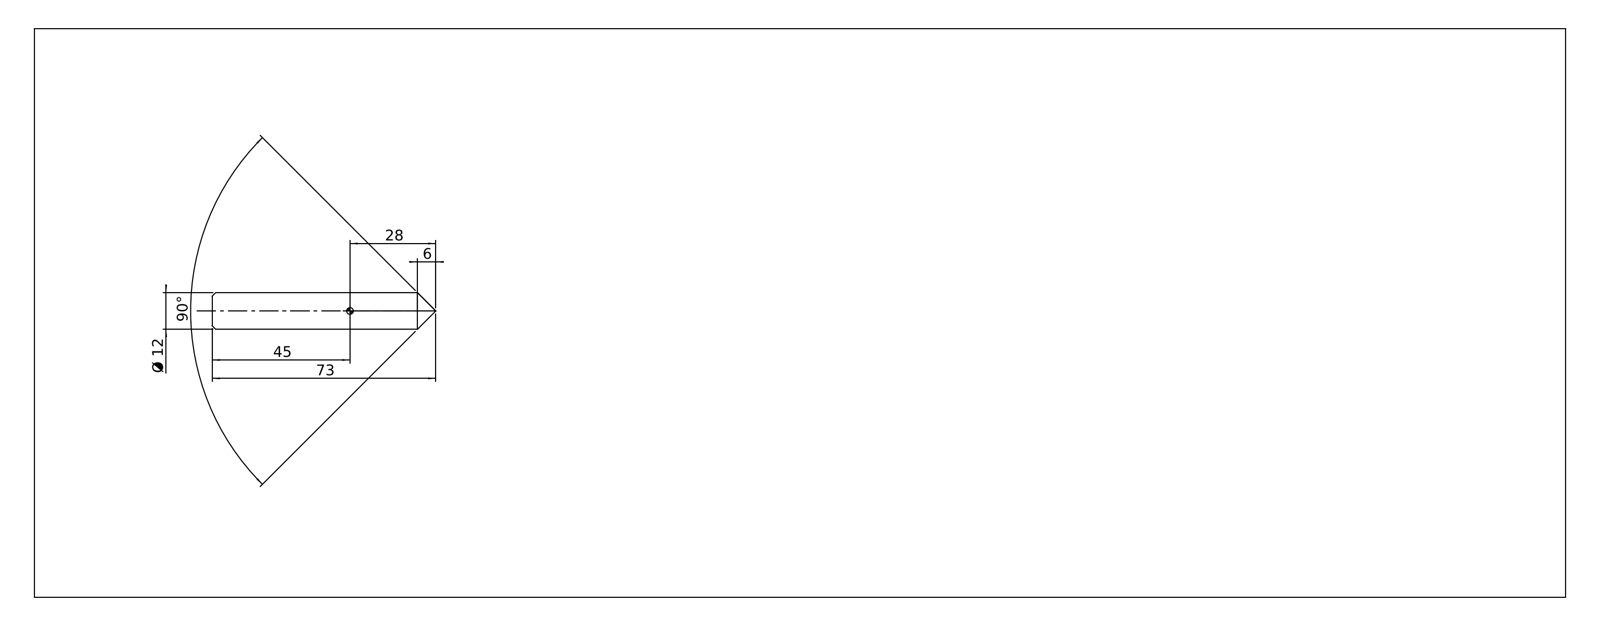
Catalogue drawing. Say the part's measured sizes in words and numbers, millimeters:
The part is named "890.120.00". Its 3-D file was written by "SolidWorks 2019 (CONFIG_CONTROL_DESIGN)". It is 2 solids with 6 faces: 3 planar, 1 cylindrical and 2 other. Overall it measures 73 by 12 by 12 millimeters. Its volume is 7 778 cubic millimeters and its surface area 2 997 square millimeters. Round bosses or shafts: 1 of diameter 12. The main face-to-face distances are 67.
